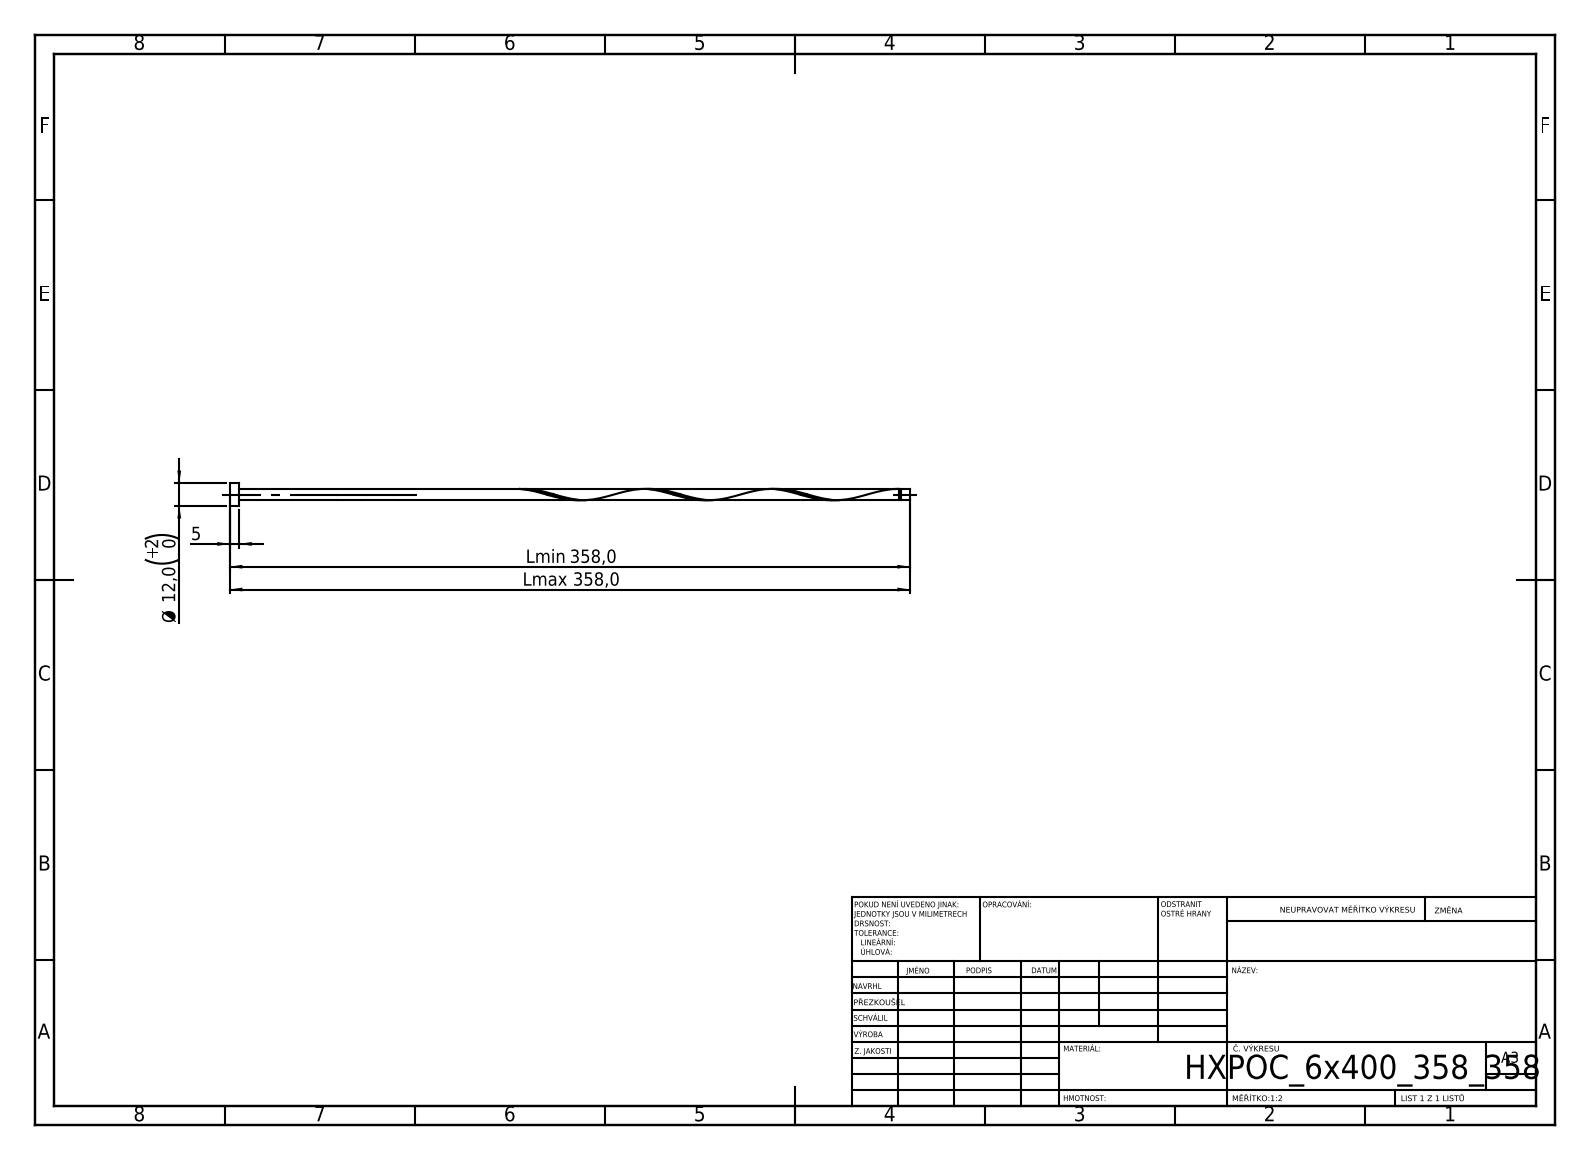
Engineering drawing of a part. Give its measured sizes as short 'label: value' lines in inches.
written by: SolidWorks 2019 (CONFIG_CONTROL_DESIGN)
unit: in
bodies: 1 solid, 16 faces (6 planar, 9 cylindrical, 1 other)
size: 14.094 × 0.472 × 0.472
volume: 0.79 in³; area: 15.06 in²
bosses: 1× ⌀0.472, 1× ⌀0.236, 1× ⌀0.189
face distances: 0.197, 14.094, 13.898, 13.913, 13.716, 0.182, 13.865, 13.669, 0.047, 0.229
